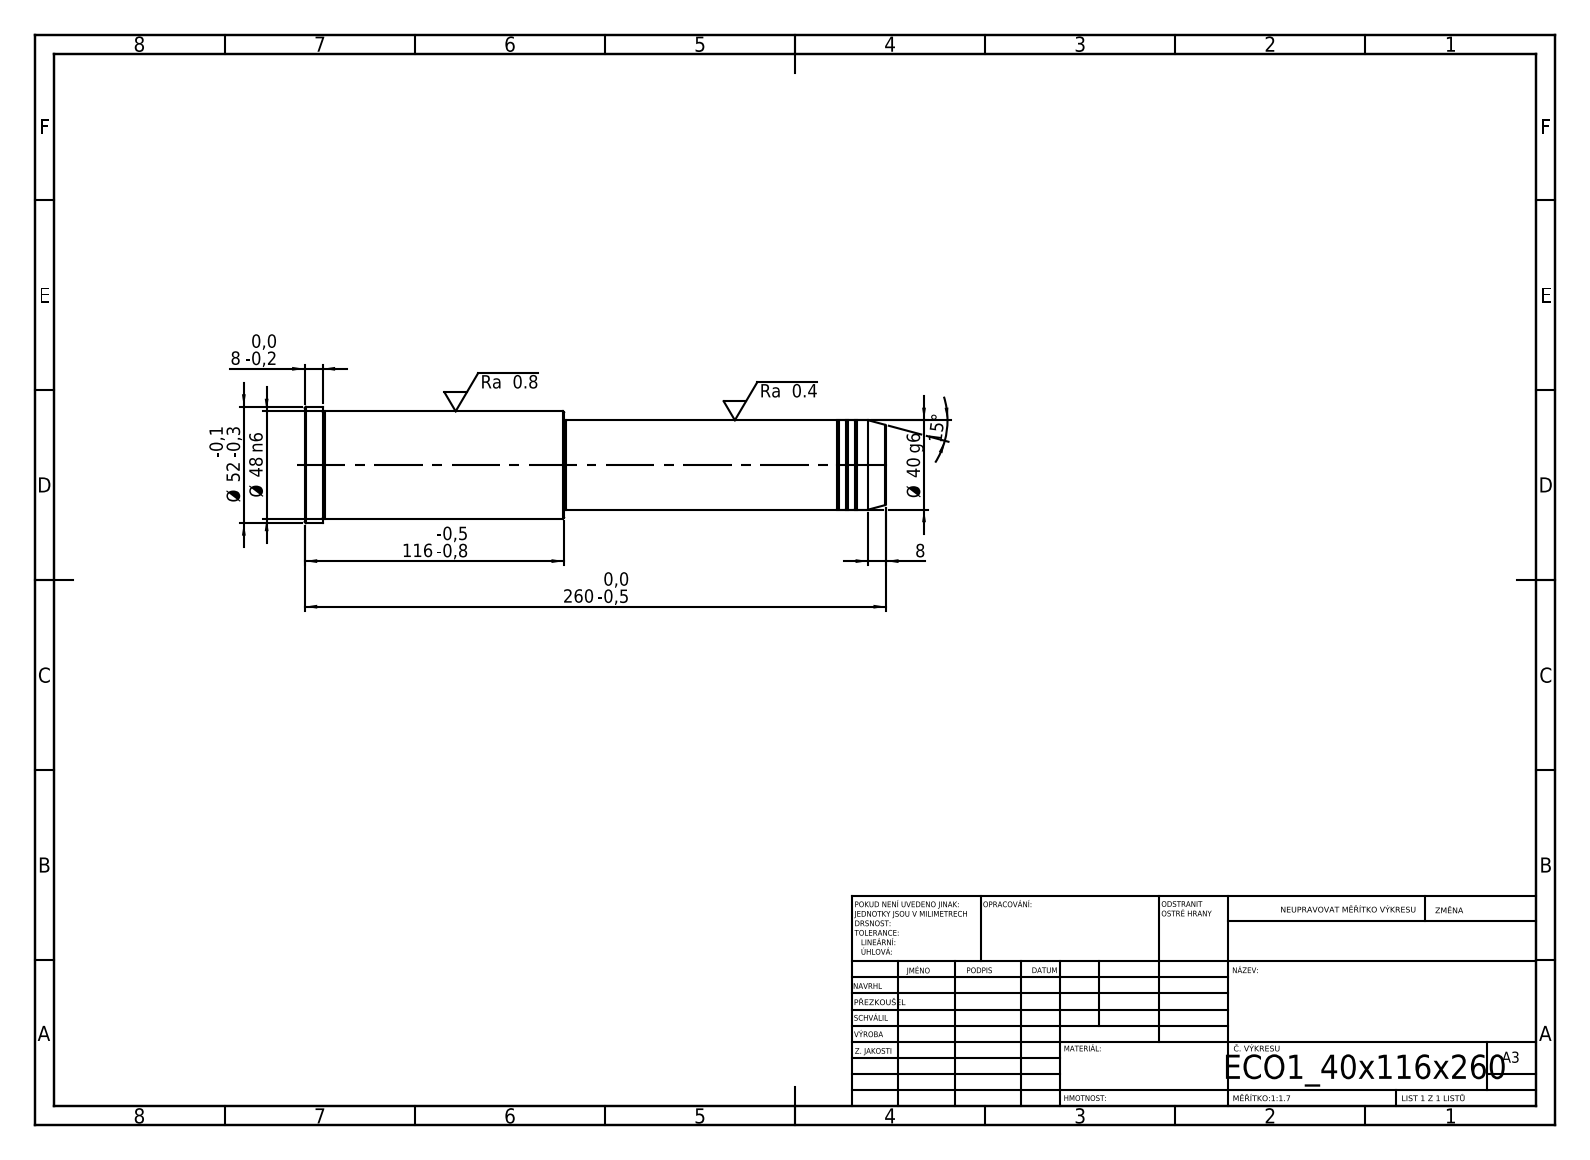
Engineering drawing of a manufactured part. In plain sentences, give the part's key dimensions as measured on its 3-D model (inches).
Its 3-D file was written by "SolidWorks 2019 (CONFIG_CONTROL_DESIGN)". It is 1 solid with 43 faces: 5 planar, 14 cylindrical and 24 other. Overall it measures 10.236 by 2.047 by 2.047 inches. Its volume is 23.92 cubic inches and its surface area 61.95 square inches. Round bosses or shafts: 1 of diameter 2.047, 1 of diameter 1.89, 1 of diameter 1.575, 1 of diameter 1.535. The main face-to-face distances are 10.236, 5.669, 4.567, 9.921, 4.252, 0.315, 5.63, 0.039, 4.291, 4.606.
